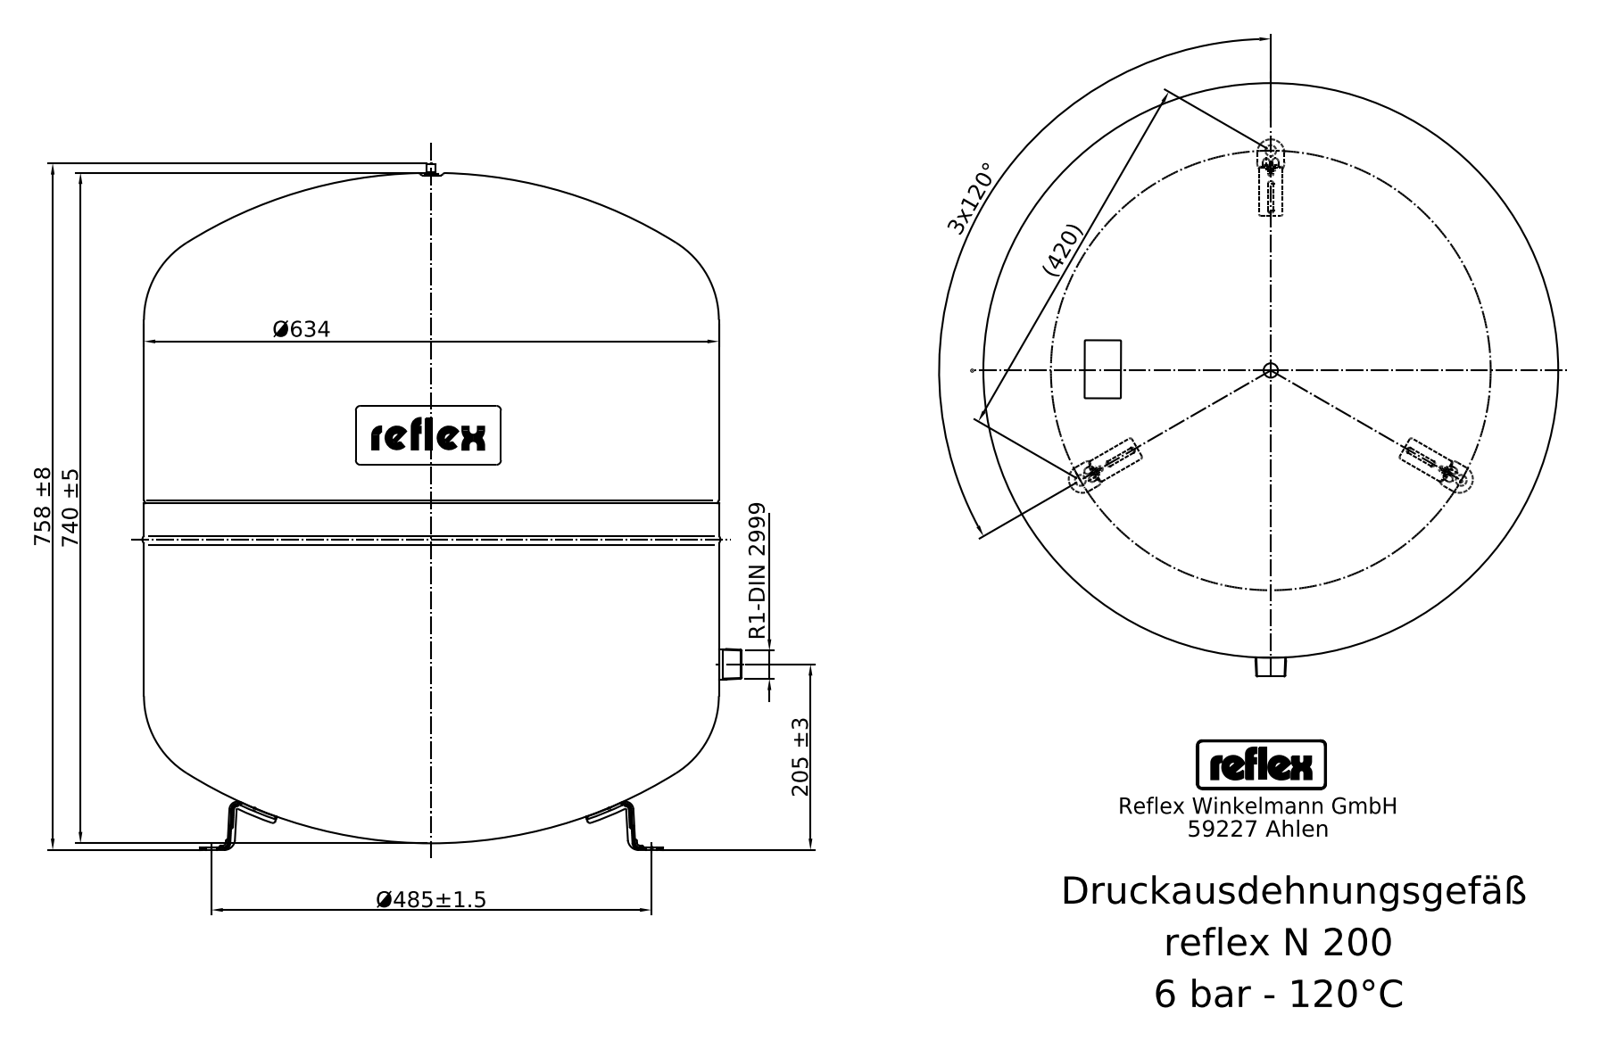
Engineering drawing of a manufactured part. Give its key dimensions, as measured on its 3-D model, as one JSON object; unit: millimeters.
{"step_written_by": "Mechanical Desktop 2008 (CONFIG_CONTROL_DESIGN)", "units": "millimeters", "bodies": {"solids": 16, "faces": 245, "planar": 100, "cylindrical": 90, "other": 55}, "overall_size": [785, 664.46, 644.91], "volume_mm3": 206600000, "surface_area_mm2": 3157000, "round_holes": [[13.4, 3], [5.64, 1], [25.7, 1]], "round_bosses_or_shafts": [[634.01, 1], [634, 1], [33.7, 1], [6.84, 1], [3.6, 1], [2.4, 1]], "partial_cylinders_radius": [[1, 15], [2.5, 15], [5, 15], [3.94, 4], [1.57, 3], [2.69, 2], [4.72, 2], [6.49, 2]], "face_to_face_distances": [441, 2.5, 47.5, 220.5, 45, 50, 172, 392.5, 613, 2], "hole_center_spacings": [242.5, 420.02]}
